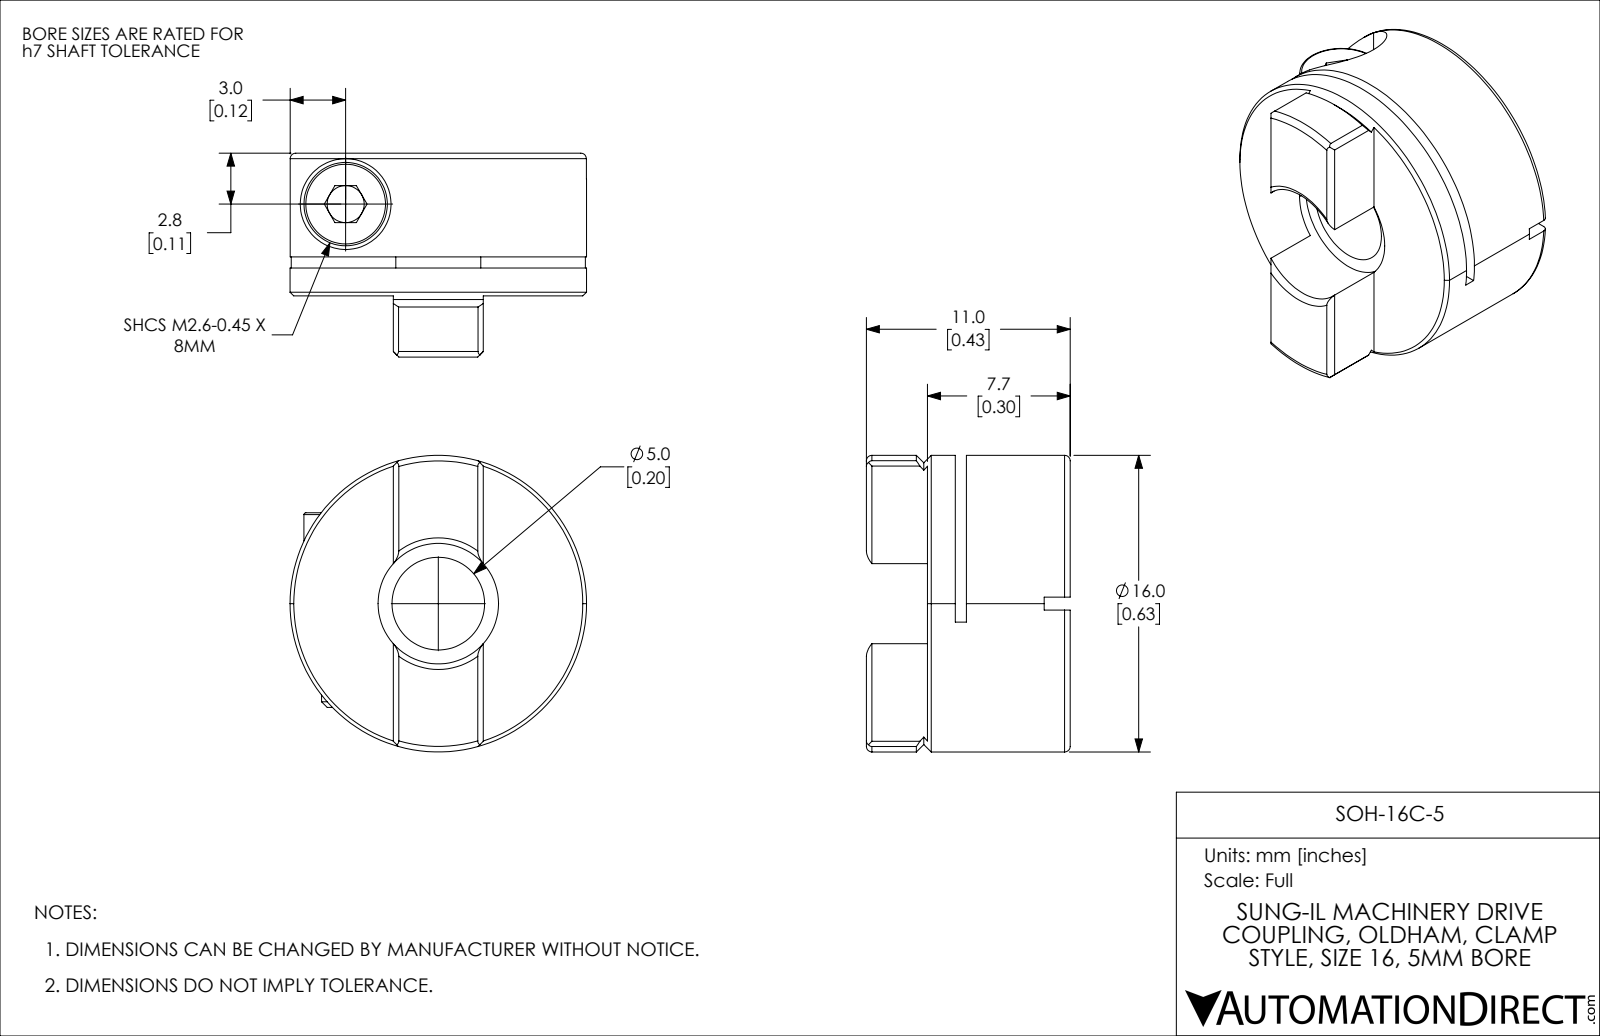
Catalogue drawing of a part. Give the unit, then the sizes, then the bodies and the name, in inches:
Units: inches
Overall size (bounding box): 0.63 × 0.63 × 0.433
Round holes (diameter × count): ⌀0.079 ×1, ⌀0.081 ×1, ⌀0.11 ×1, ⌀0.193 ×1, ⌀0.197 ×1, ⌀0.256 ×1
Round bosses / shafts (diameter × count): ⌀0.63 ×1, ⌀0.177 ×1, ⌀0.102 ×1
Partial cylindrical surfaces — rounded edges, fillets, slot ends (radius × count): R0.886 ×1
Main face-to-face distances: 0.303, 0.244, 0.059, 0.22, 0.024, 0.083, 0.028, 0.189, 0.433, 0.213
Volume: 0.087 in³ · Surface area: 2.297 in²
Bodies: 2 solids, 93 faces (44 planar, 25 cylindrical, 24 other)
Part name (STEP PRODUCT): SOH-16C-5
STEP written by: SolidWorks 2021 (CONFIG_CONTROL_DESIGN)
